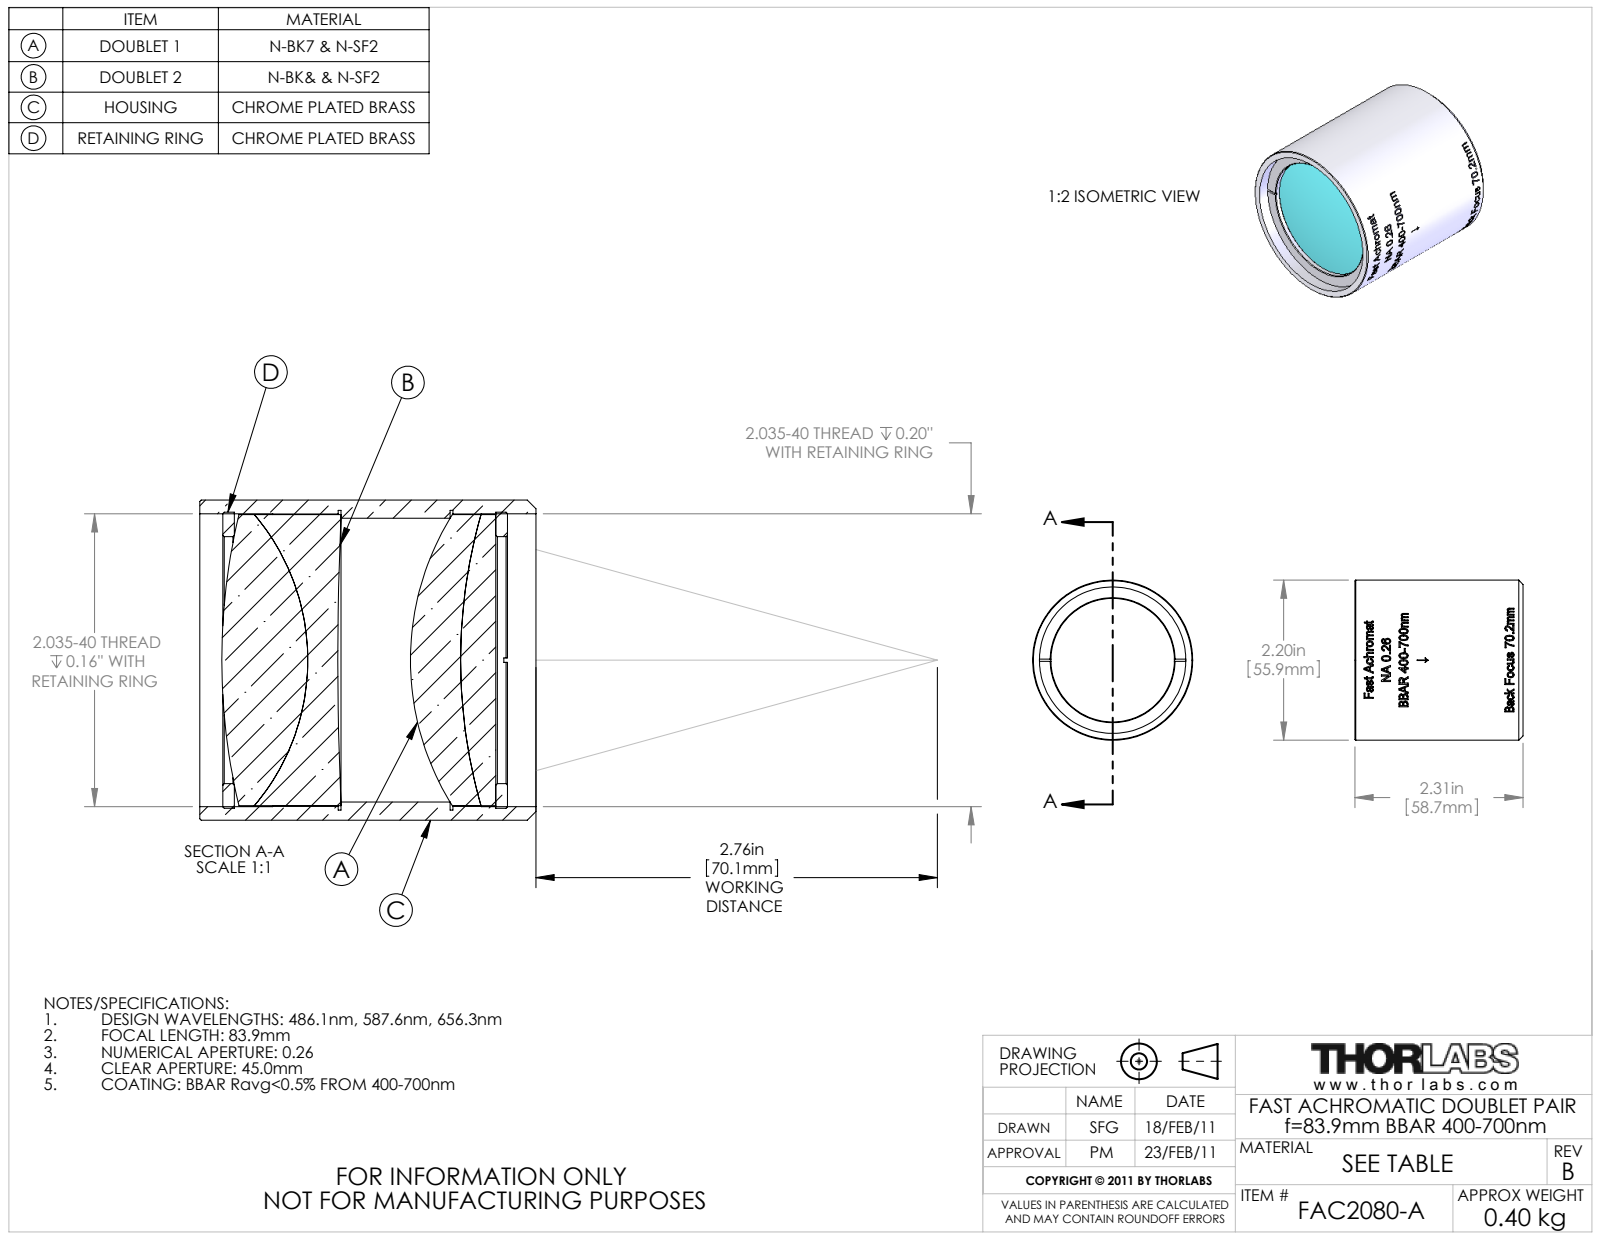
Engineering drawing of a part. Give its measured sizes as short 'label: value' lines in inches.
name: 20562-E0W
written by: SolidWorks 2009 (AUTOMOTIVE_DESIGN)
unit: in
bodies: 7 solids, 197 faces (25 planar, 138 cylindrical, 34 other)
size: 2.311 × 2.2 × 2.2
volume: 5.489 in³; area: 70.79 in²
holes: 1× ⌀1.697, 1× ⌀1.95, 1× ⌀2.008, 1× ⌀2.012, 1× ⌀2.06
bosses: 1× ⌀2.2, 1× ⌀2.035, 1× ⌀2
face distances: 1.797, 0.08, 1.877, 1.957, 1.878, 0.08, 2.115, 2.035, 0.238, 0.158
